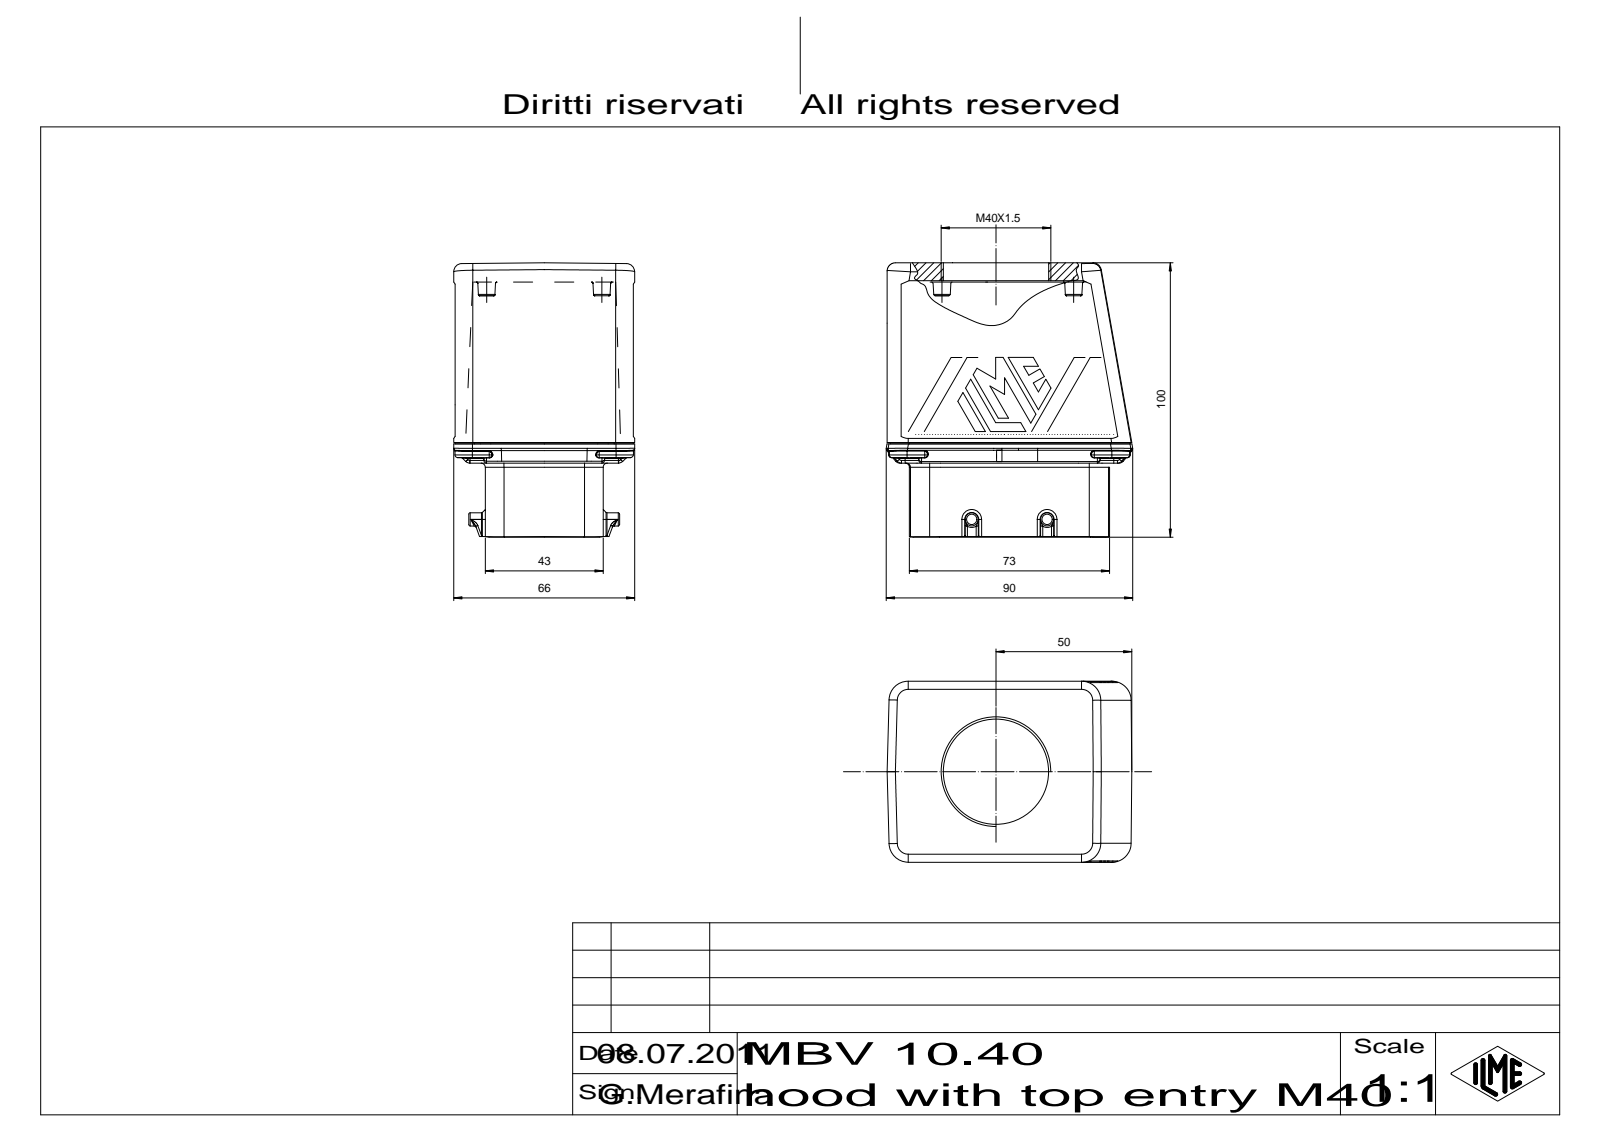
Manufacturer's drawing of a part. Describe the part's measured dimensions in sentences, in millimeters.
The part is named "53848_Body_1_Body_1.1". Its 3-D file was written by "CoCreate Modeling 16.00A 16-Aug-2008 (C) Parametric Technology GmbH (AUTOMOTIVE_DESIGN)". It is 1 solid with 609 faces: 297 planar, 148 cylindrical and 164 other. Overall it measures 99.49 by 88.76 by 66.01 millimeters. Its volume is 377 944 cubic millimeters and its surface area 46 921 square millimeters. Round holes: 1 of diameter 40. Round bosses or shafts: 2 of diameter 4.8. Partial cylindrical surfaces (rounded edges, fillets, slot ends): 46 of radius 1, 18 of radius 0.3, 12 of radius 7, 10 of radius 3, 8 of radius 0.5, 6 of radius 1.5, 4 of radius 4.2, 4 of radius 5. The main face-to-face distances are 72.73, 65.01, 0.4, 65.41, 11, 54.01, 54, 43, 11.01, 25.
